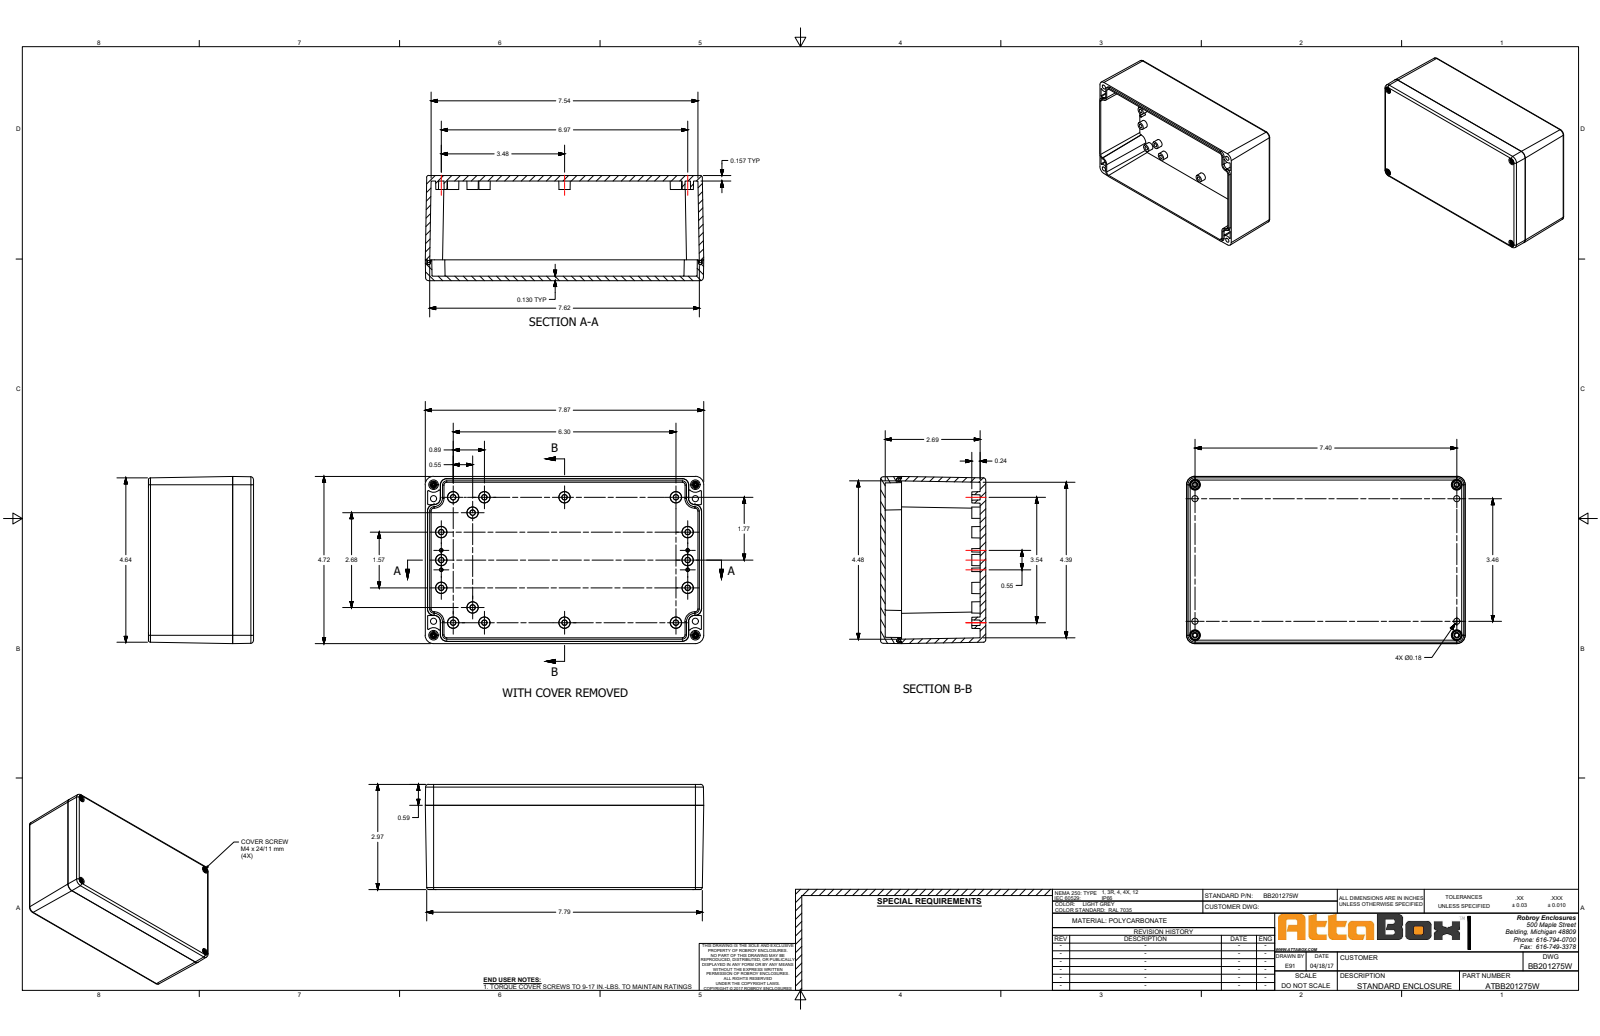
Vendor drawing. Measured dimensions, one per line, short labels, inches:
name: BB201275W
written by: SolidWorks 2018 (AUTOMOTIVE_DESIGN)
unit: in
bodies: 11 solids, 1691 faces (631 planar, 436 cylindrical, 624 other)
size: 7.874 × 4.724 × 2.972
volume: 20.31 in³; area: 334.8 in²
holes: 4× ⌀0.128, 4× ⌀0.177, 4× ⌀0.189, 4× ⌀0.197, 4× ⌀0.201, 4× ⌀0.276, 4× ⌀0.295, 4× ⌀0.307
bosses: 4× ⌀0.268, 4× ⌀0.173, 4× ⌀0.157, 4× ⌀0.13
rounds: 48× R0.039, 38× R0.02, 8× R0.104, 8× R0.203, 4× R0.059, 4× R0.079, 4× R0.102, 4× R0.122
face distances: 0.126, 2.972, 2.843, 0.13, 0.157, 2.685, 2.815, 4.724, 4.598, 4.551
hole spacings: 0.394, 3.858, 7.402, 7.412, 8.347, 3.465, 4.252, 8.172
